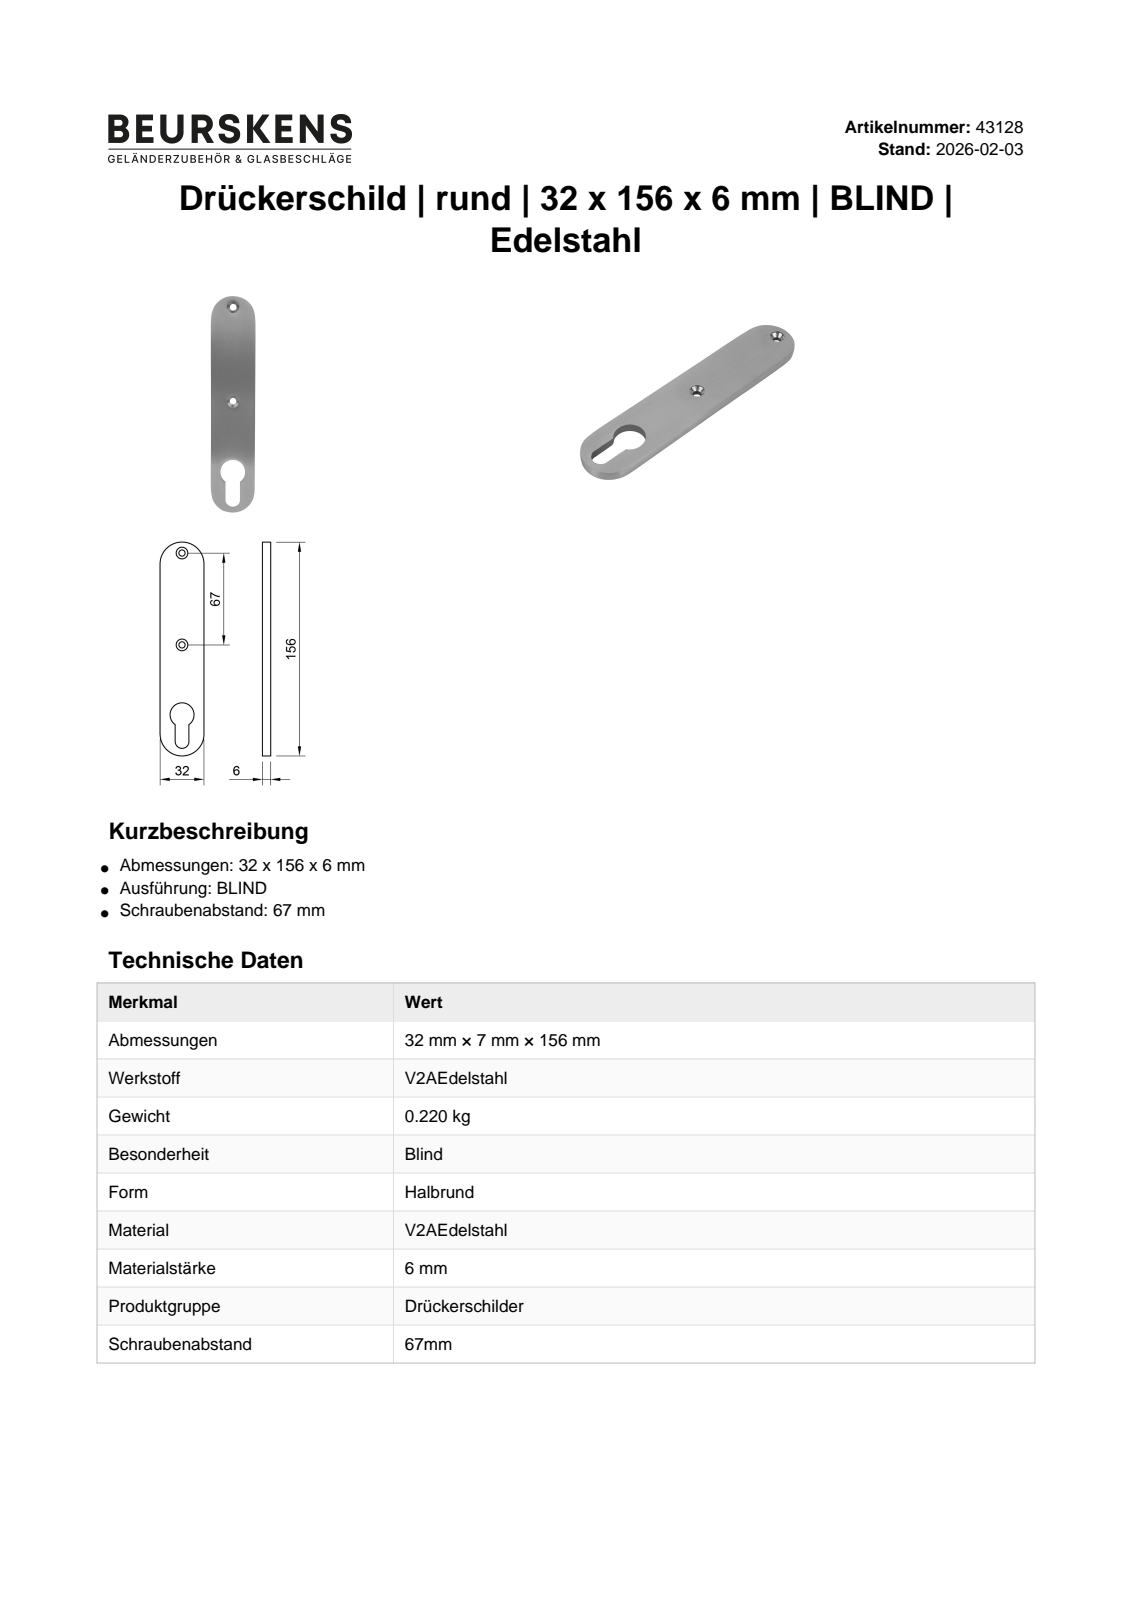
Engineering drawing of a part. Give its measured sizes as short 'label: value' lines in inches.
name: 43128
written by: Autodesk Inventor 2022 (AUTOMOTIVE_DESIGN)
unit: in
bodies: 1 solid, 14 faces (6 planar, 6 cylindrical, 2 other)
size: 6.142 × 1.26 × 0.236
volume: 1.588 in³; area: 17.74 in²
holes: 2× ⌀0.177, 1× ⌀0.689
rounds: 2× R0.63, 1× R0.197
face distances: 0.236, 1.26, 0.433, 0.827, 0.394
hole spacings: 2.008, 2.638, 4.646
